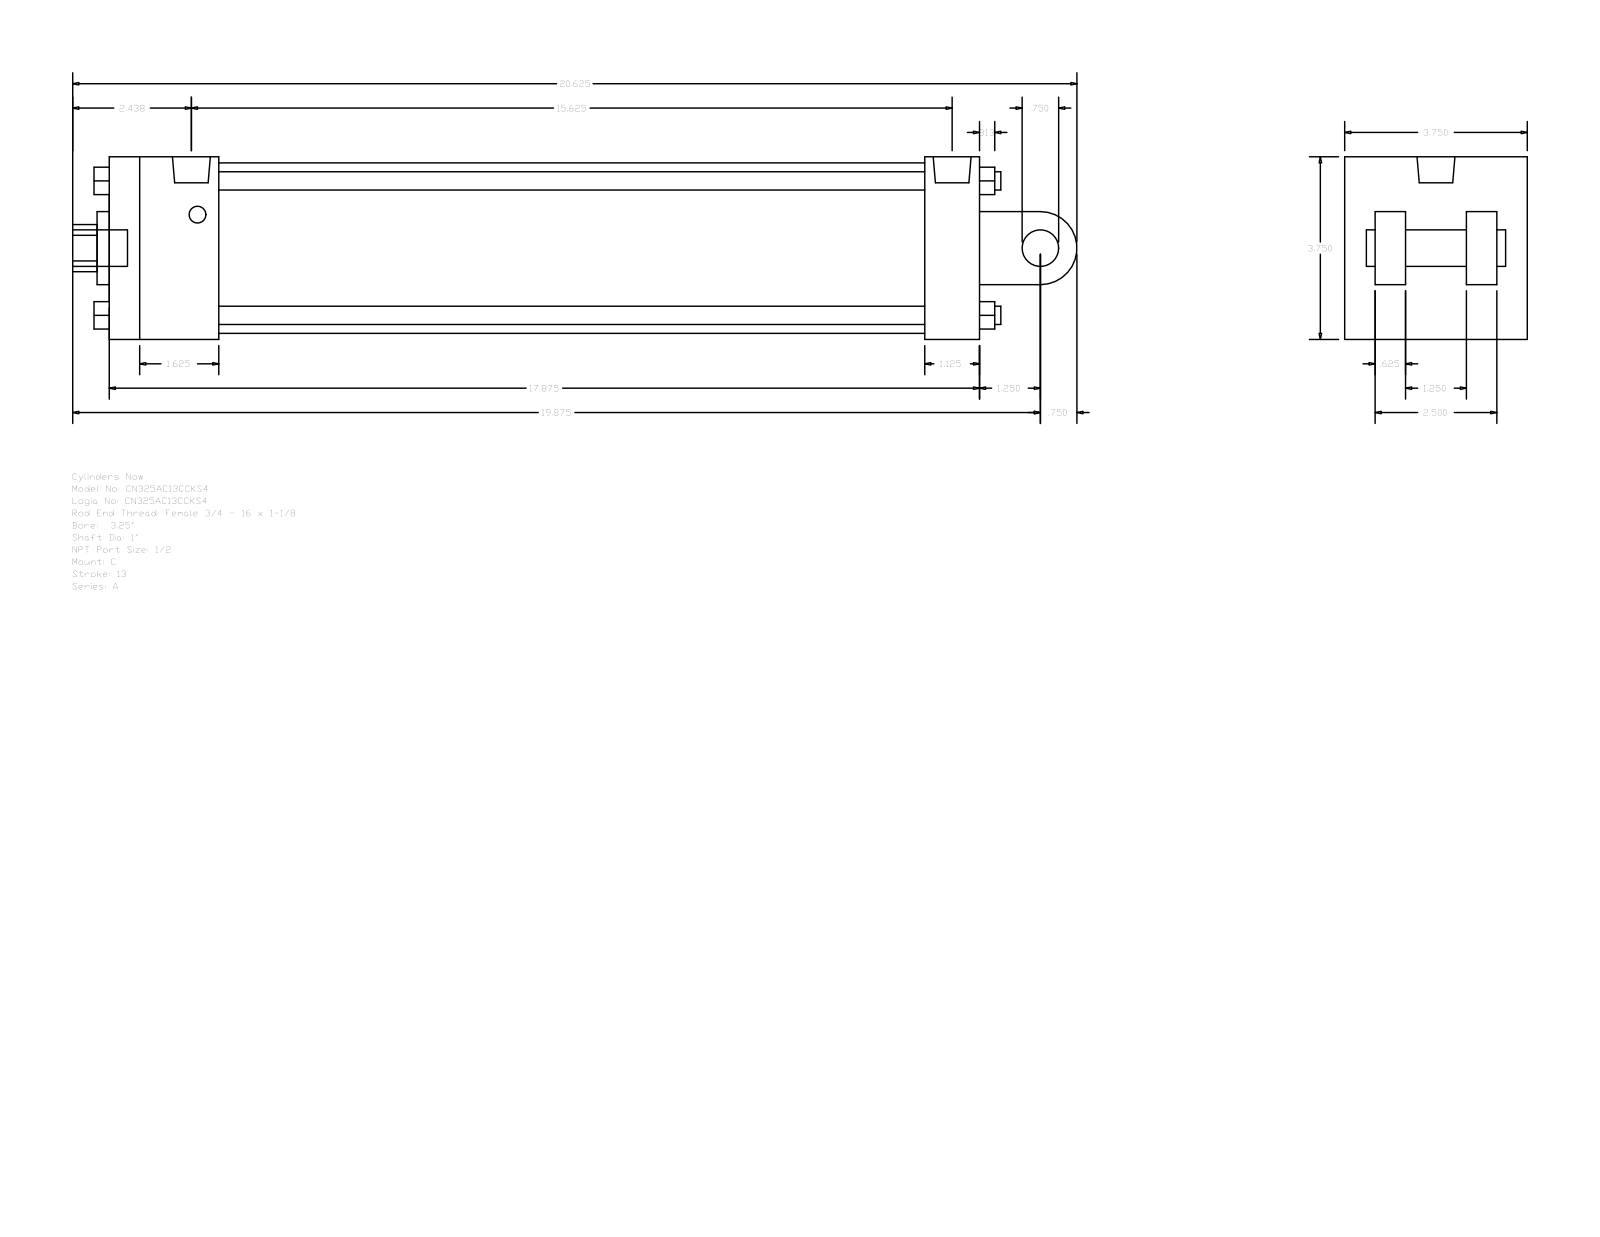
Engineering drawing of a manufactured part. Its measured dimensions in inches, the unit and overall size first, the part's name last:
Units: inches
Overall size (bounding box): 20.625 × 3.75 × 3.75
Round holes (diameter × count): ⌀0.344 ×2, ⌀0.778 ×1, ⌀1 ×1, ⌀1.5 ×1, ⌀3.5 ×1
Round bosses / shafts (diameter × count): ⌀0.375 ×4, ⌀0.75 ×2, ⌀0.344 ×2, ⌀0.778 ×1
Partial cylindrical surfaces — rounded edges, fillets, slot ends (radius × count): R0.484 ×1, R0.75 ×1
Main face-to-face distances: 3.75, 17.875, 0.625, 2.5, 1.125, 1.875, 3.125, 1.25, 2.625, 16.75
Hole centre spacings: 0.125
Bodies: 0 solids, 135 faces (102 planar, 33 cylindrical, 0 other)
Part name (STEP PRODUCT): A_C__0325_1
STEP written by: GSSL Pune (CONFIG_CONTROL_DESIGN)
